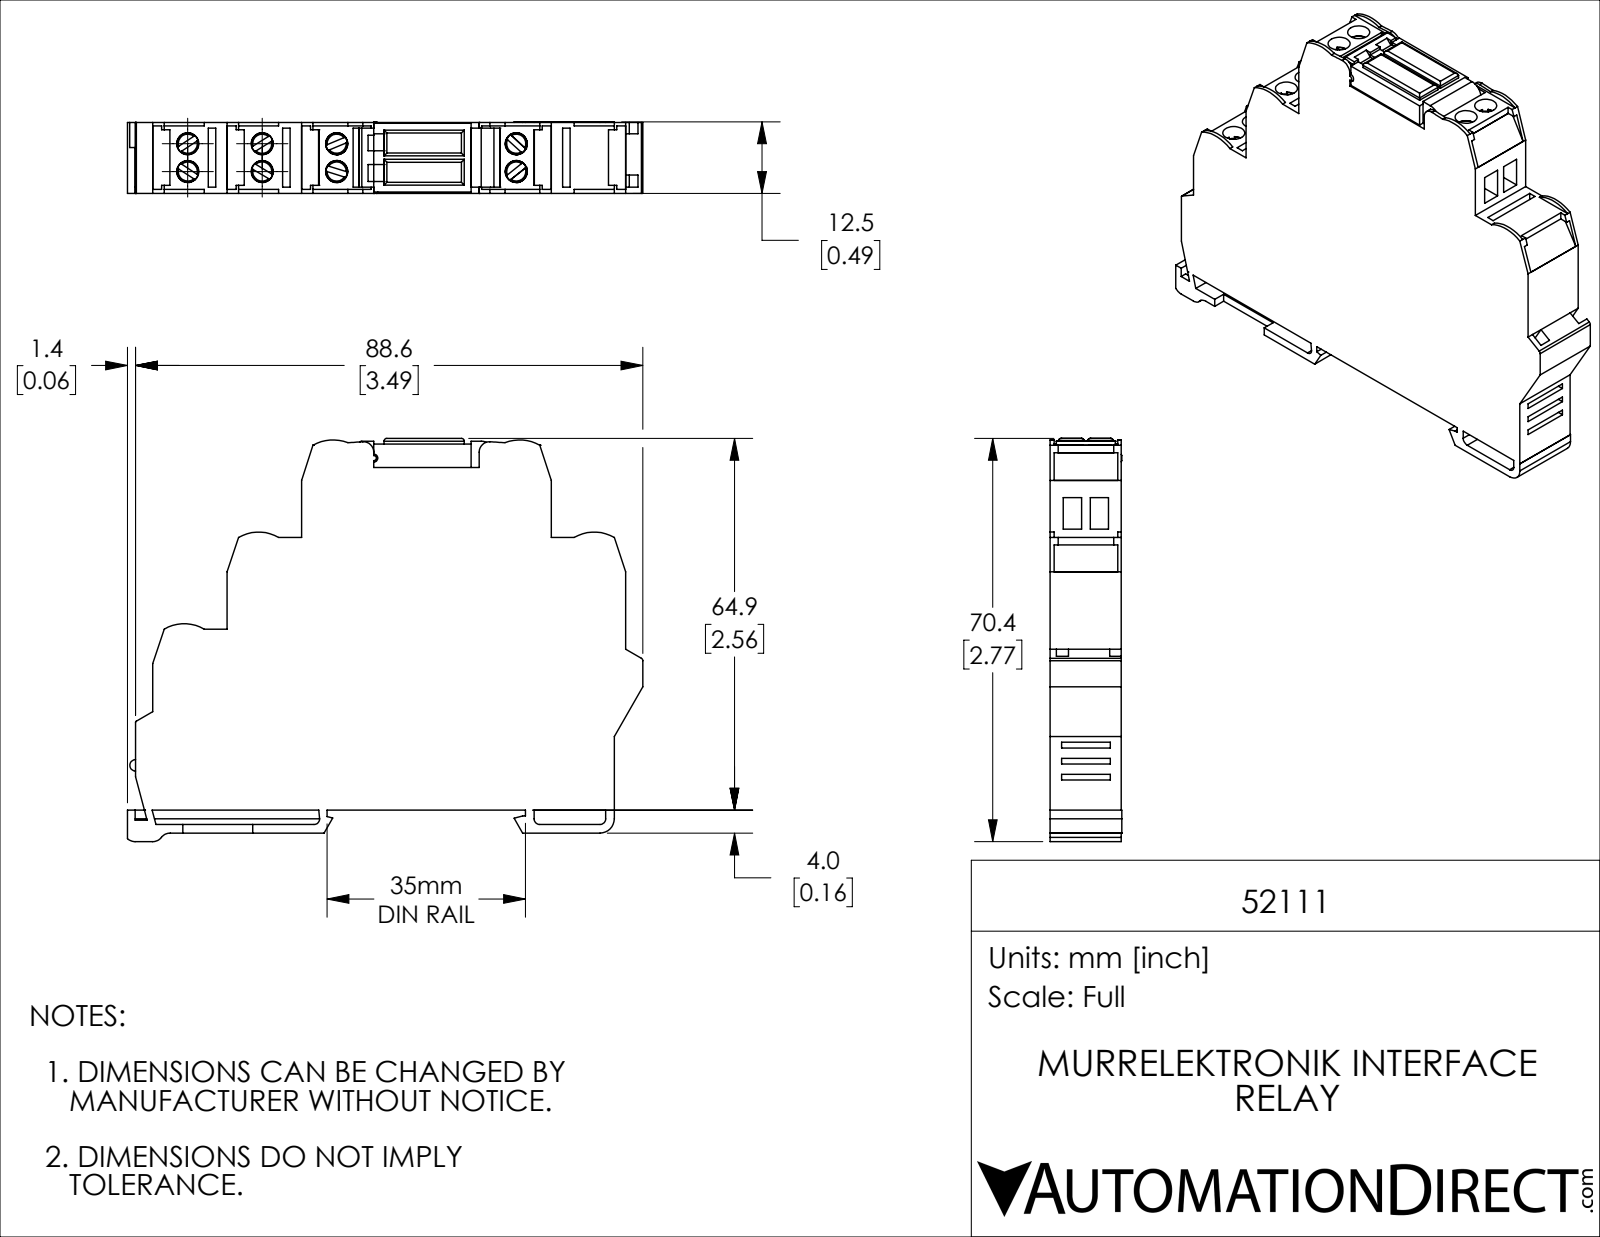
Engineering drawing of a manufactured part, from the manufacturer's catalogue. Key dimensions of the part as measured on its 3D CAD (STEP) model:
Part name (STEP PRODUCT): 52111
STEP written by: SolidWorks 2019 (CONFIG_CONTROL_DESIGN)
Units: inches
Bodies: 1 solid, 419 faces (315 planar, 78 cylindrical, 26 other)
Overall size (bounding box): 3.543 × 2.772 × 0.492
Volume: 3.294 in³ · Surface area: 27.11 in²
Round holes (diameter × count): ⌀0.152 ×8
Round bosses / shafts (diameter × count): ⌀0.148 ×8
Partial cylindrical surfaces — rounded edges, fillets, slot ends (radius × count): R0.02 ×9, R0.276 ×5, R0.039 ×4, R0.079 ×3, R0.028 ×2, R0.071 ×2, R0.089 ×2, R0.012 ×1
Main face-to-face distances: 0.488, 0.059, 0.157, 0.039, 0.098, 0.217, 0.185, 0.126, 0.207, 1.874
Hole centre spacings: 0.512, 0.191, 0.546, 1.024, 1.041, 1.235, 1.249, 1.746
